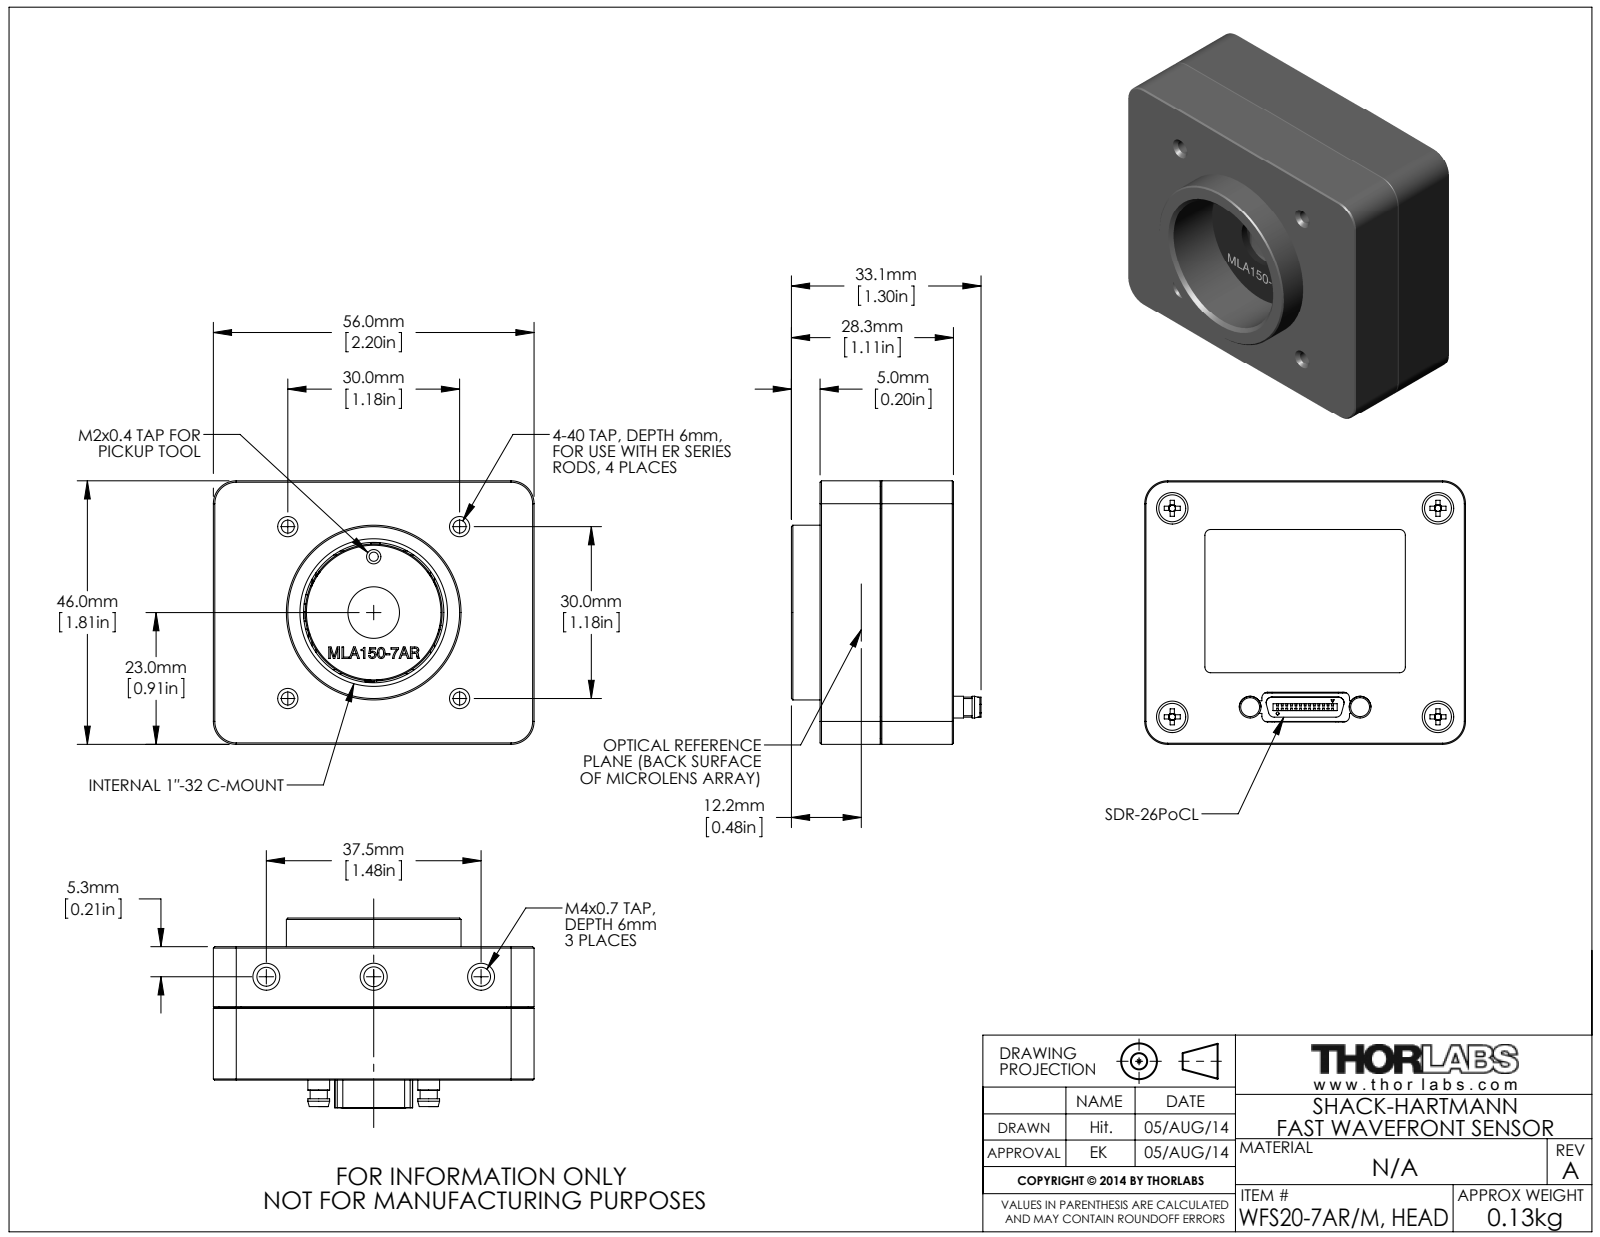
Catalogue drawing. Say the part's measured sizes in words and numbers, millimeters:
The part is named "Stift 1x4; MTN003852; Halter Teil1 WFS20 Baugruppe; Halter Teil3 TYP150-7AR Baugruppe (+8 more)". Its 3-D file was written by "SolidWorks 2014 (AUTOMOTIVE_DESIGN)". It is 41 solids with 2364 faces: 1144 planar, 649 cylindrical and 571 other. Overall it measures 56 by 46 by 33.11 millimeters. Its volume is 71 068 cubic millimeters and its surface area 43 184 square millimeters. Round holes: 26 of diameter 0.6, 6 of diameter 3.2, 4 of diameter 2.05, 4 of diameter 2.26, 4 of diameter 2.7, 4 of diameter 2.9, 4 of diameter 3, 4 of diameter 6, 3 of diameter 1.9, 2 of diameter 1.2, 2 of diameter 1.75, 2 of diameter 3.3. Round bosses or shafts: 108 of diameter 0.7, 11 of diameter 1, 8 of diameter 3, 4 of diameter 5.6, 4 of diameter 4.7, 4 of diameter 2.5, 4 of diameter 2.1, 2 of diameter 3.8. Partial cylindrical surfaces (rounded edges, fillets, slot ends): 19 of radius 1, 12 of radius 2, 6 of radius 0.18, 4 of radius 0.2, 4 of radius 2.75, 4 of radius 3.1, 4 of radius 3.5, 4 of radius 3.8. The main face-to-face distances are 14.98, 16.59, 1.61, 3.5, 19.39, 3.9, 13.5, 1.48, 3.09, 1. The hole center spacings are 1.4, 1.6, 2.66, 5.72, 3.2, 3.5, 4.16, 4.46.
